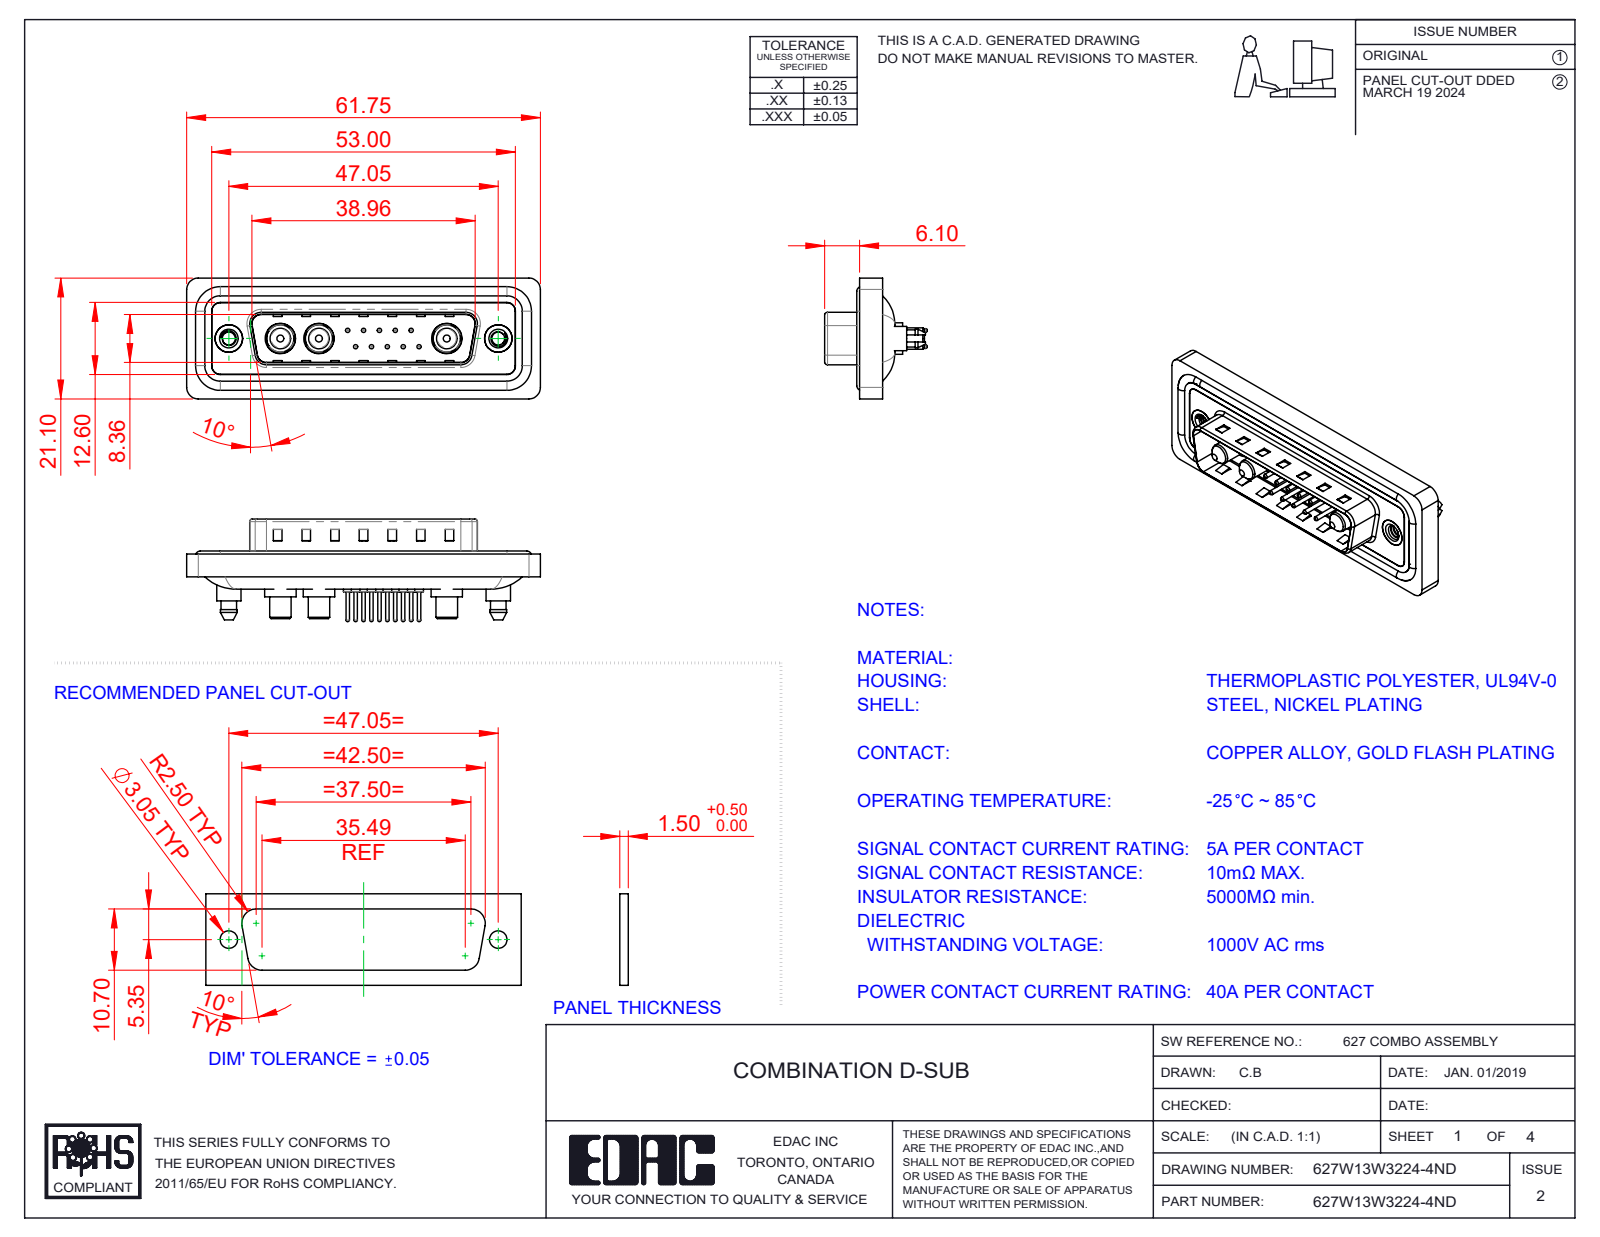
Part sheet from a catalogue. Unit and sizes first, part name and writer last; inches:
Units: inches
Overall size (bounding box): 2.431 × 0.831 × 0.705
Round holes (diameter × count): ⌀0.03 ×10, ⌀0.063 ×10, ⌀0.079 ×10, ⌀0.191 ×3, ⌀0.209 ×3, ⌀0.089 ×2, ⌀0.157 ×2, ⌀0.189 ×2, ⌀0.197 ×2
Round bosses / shafts (diameter × count): ⌀0.059 ×10, ⌀0.024 ×10, ⌀0.063 ×4, ⌀0.217 ×3, ⌀0.205 ×3, ⌀0.187 ×3, ⌀0.148 ×3, ⌀0.142 ×3
Partial cylindrical surfaces — rounded edges, fillets, slot ends (radius × count): R0.059 ×24, R0.079 ×18, R0.063 ×10, R0.02 ×8, R0.01 ×4, R0.024 ×4, R0.026 ×4, R0.035 ×4
Main face-to-face distances: 0.016, 0.059, 0.043, 0.063, 0.02, 0.122, 0.114, 0.032, 0.377, 0.161
Hole centre spacings: 0.124, 0.109, 0.198, 0.218, 0.295, 0.198, 0.327, 0.398
Volume: 0.459 in³ · Surface area: 18.98 in²
Bodies: 23 solids, 1028 faces (325 planar, 425 cylindrical, 278 other)
Part name (STEP PRODUCT): 627Combo Threaded Boardlock_5; 627Combo Contact Row 1_24; Power Pin_40A S; 627Combo Housing_13W3 (+6 more)
STEP written by: SolidWorks 2023 (CONFIG_CONTROL_DESIGN)
